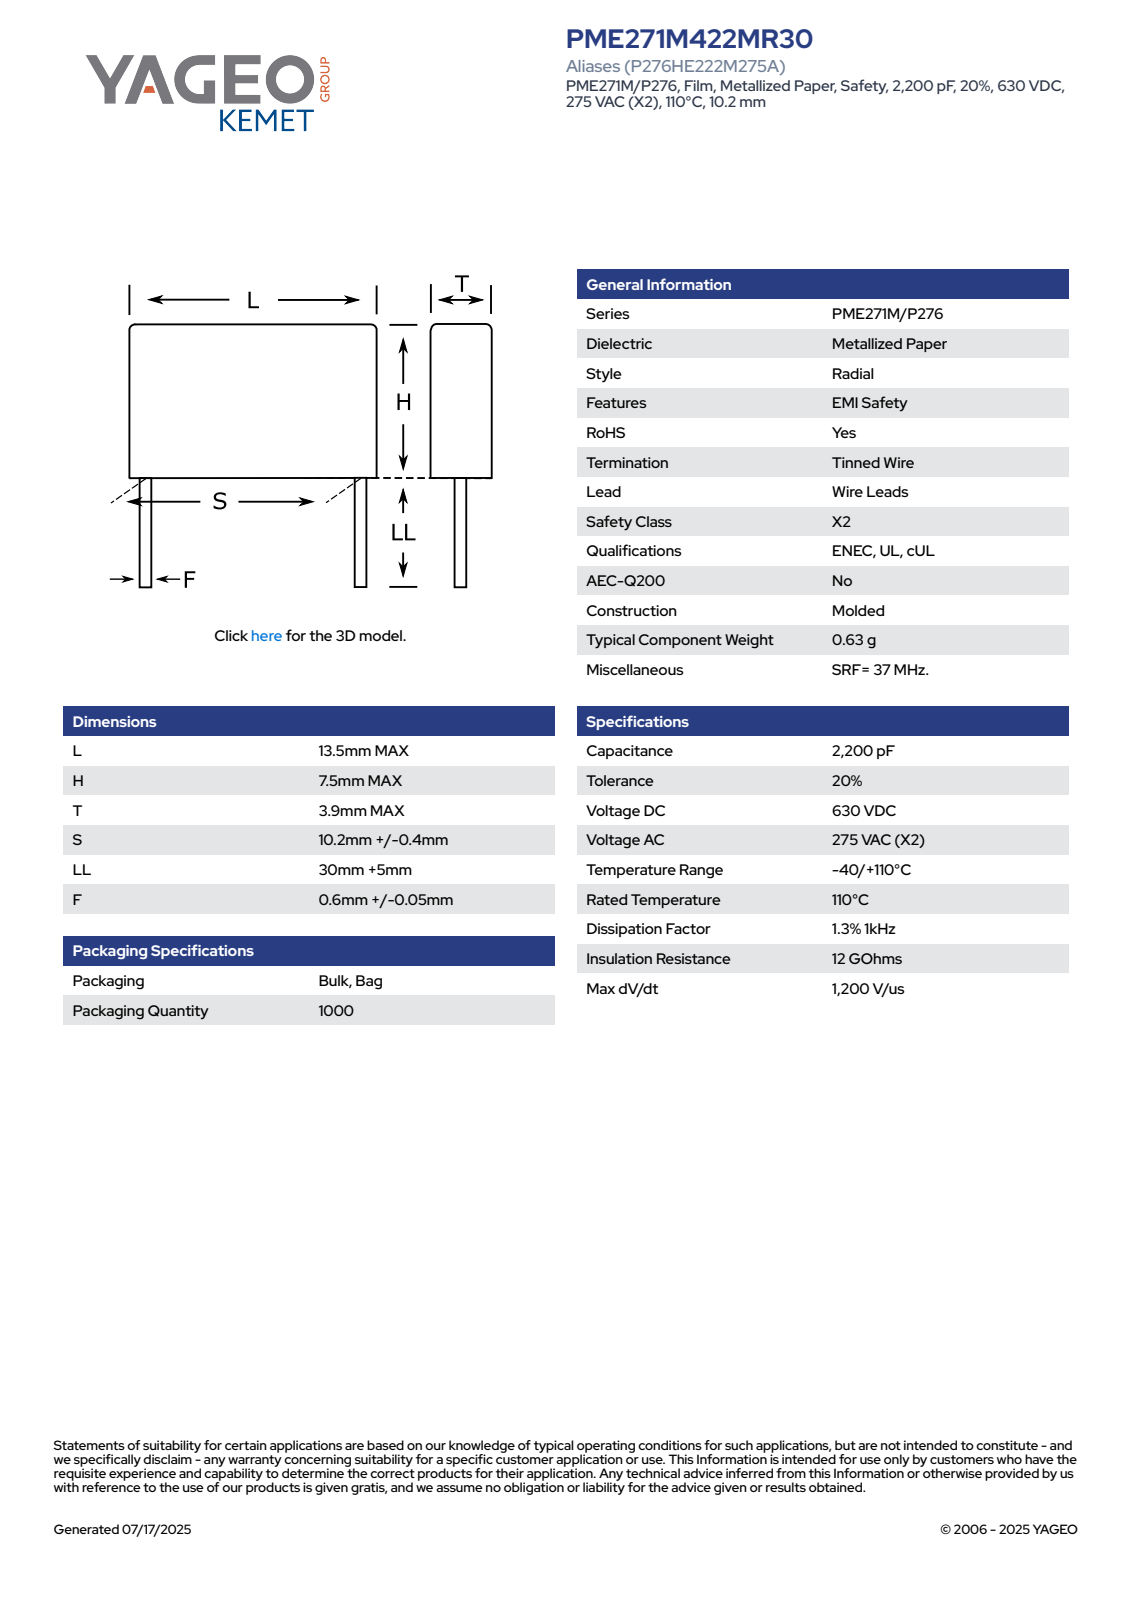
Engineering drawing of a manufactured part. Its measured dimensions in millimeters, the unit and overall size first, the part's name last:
Units: millimetres
Overall size (bounding box): 42.5 × 13.5 × 3.9
Round bosses / shafts (diameter × count): ⌀0.6 ×2
Partial cylindrical surfaces — rounded edges, fillets, slot ends (radius × count): R0.5 ×4
Main face-to-face distances: 3.9, 7.5, 13.5, 35, 42.5, 1.21, 39.35, 4.35, 3.15, 38.14
Volume: 413 mm³ · Surface area: 499 mm²
Bodies: 4 solids, 73 faces (65 planar, 8 cylindrical, 0 other)
Part name (STEP PRODUCT): CFR_MOLDED_13.5X7.5X3.9_L13.5H7.5T3.9S10.2LL35F0.6
STEP written by: SolidWorks 2014 (AUTOMOTIVE_DESIGN)
